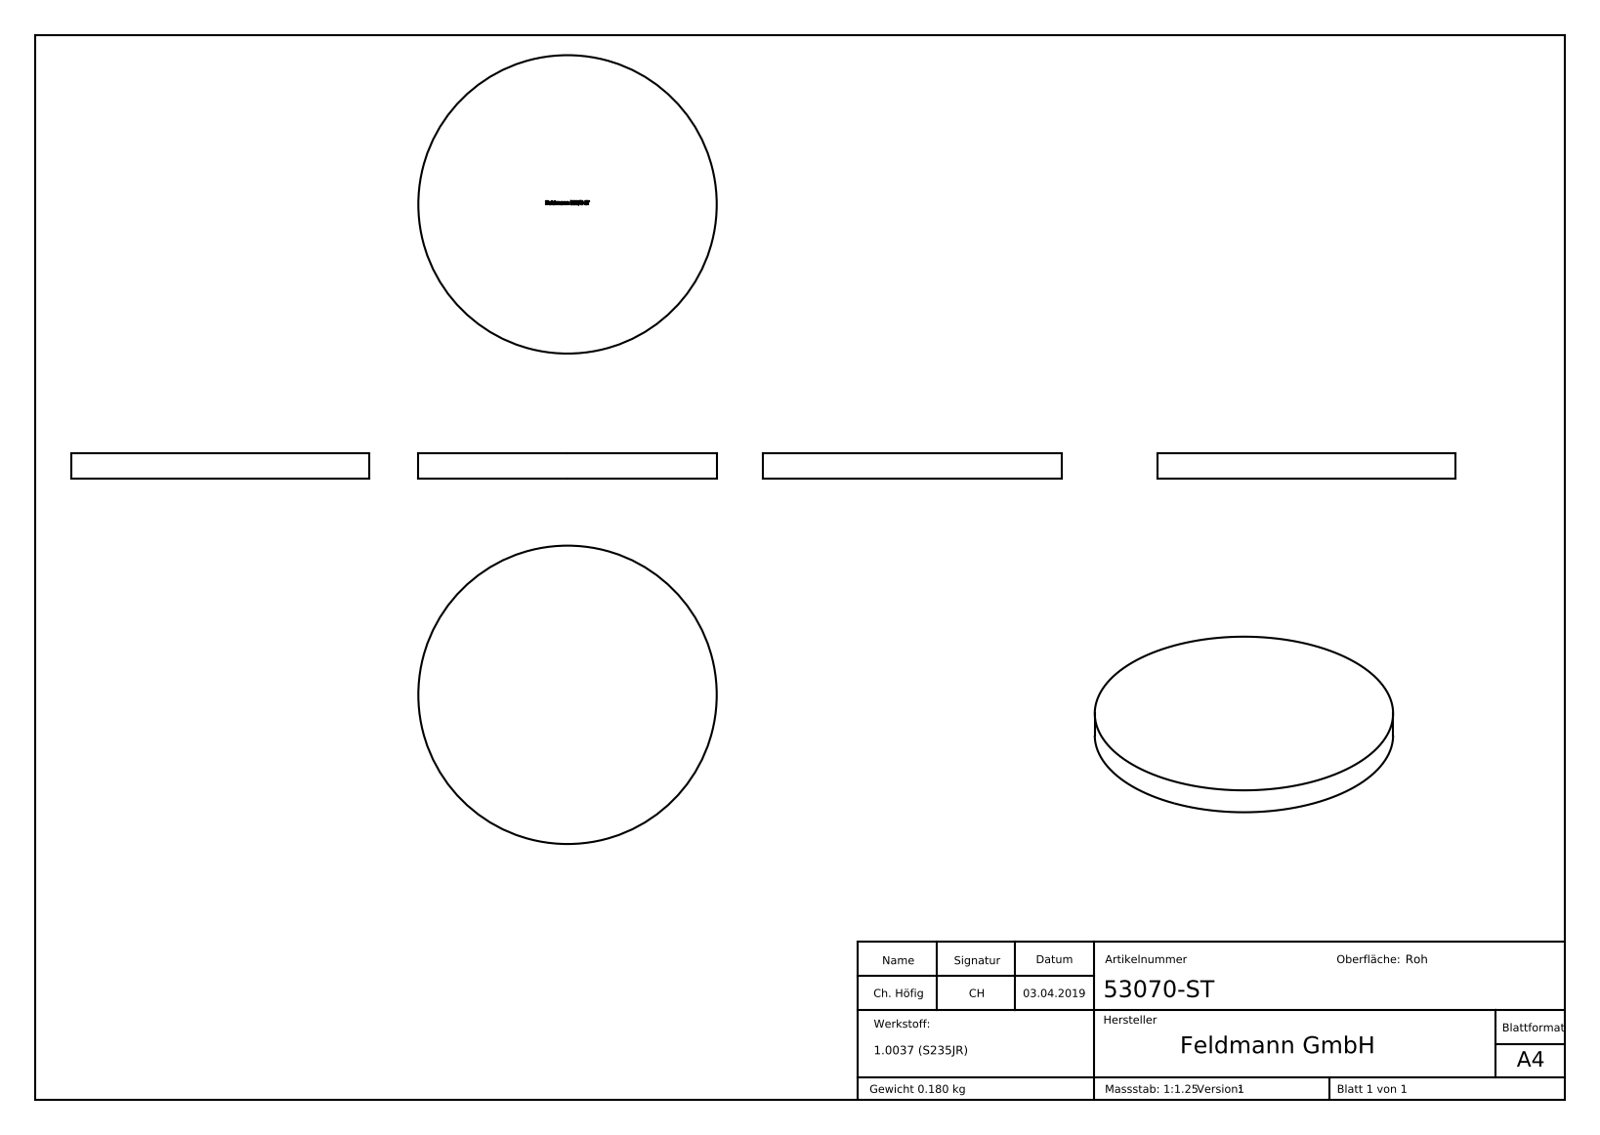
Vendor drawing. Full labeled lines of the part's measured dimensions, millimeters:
Part name (STEP PRODUCT): 53070-ST
STEP written by: SolidWorks 2015 (CONFIG_CONTROL_DESIGN)
Units: millimetres
Bodies: 1 solid, 211 faces (106 planar, 2 cylindrical, 103 other)
Overall size (bounding box): 70 × 70 × 6
Volume: 23 091 mm³ · Surface area: 9 022 mm²
Round bosses / shafts (diameter × count): ⌀70 ×1
Main face-to-face distances: 6, 5.9, 0.44, 0.99, 1.78, 0.67, 0.79, 1.21, 8.49, 9.7
